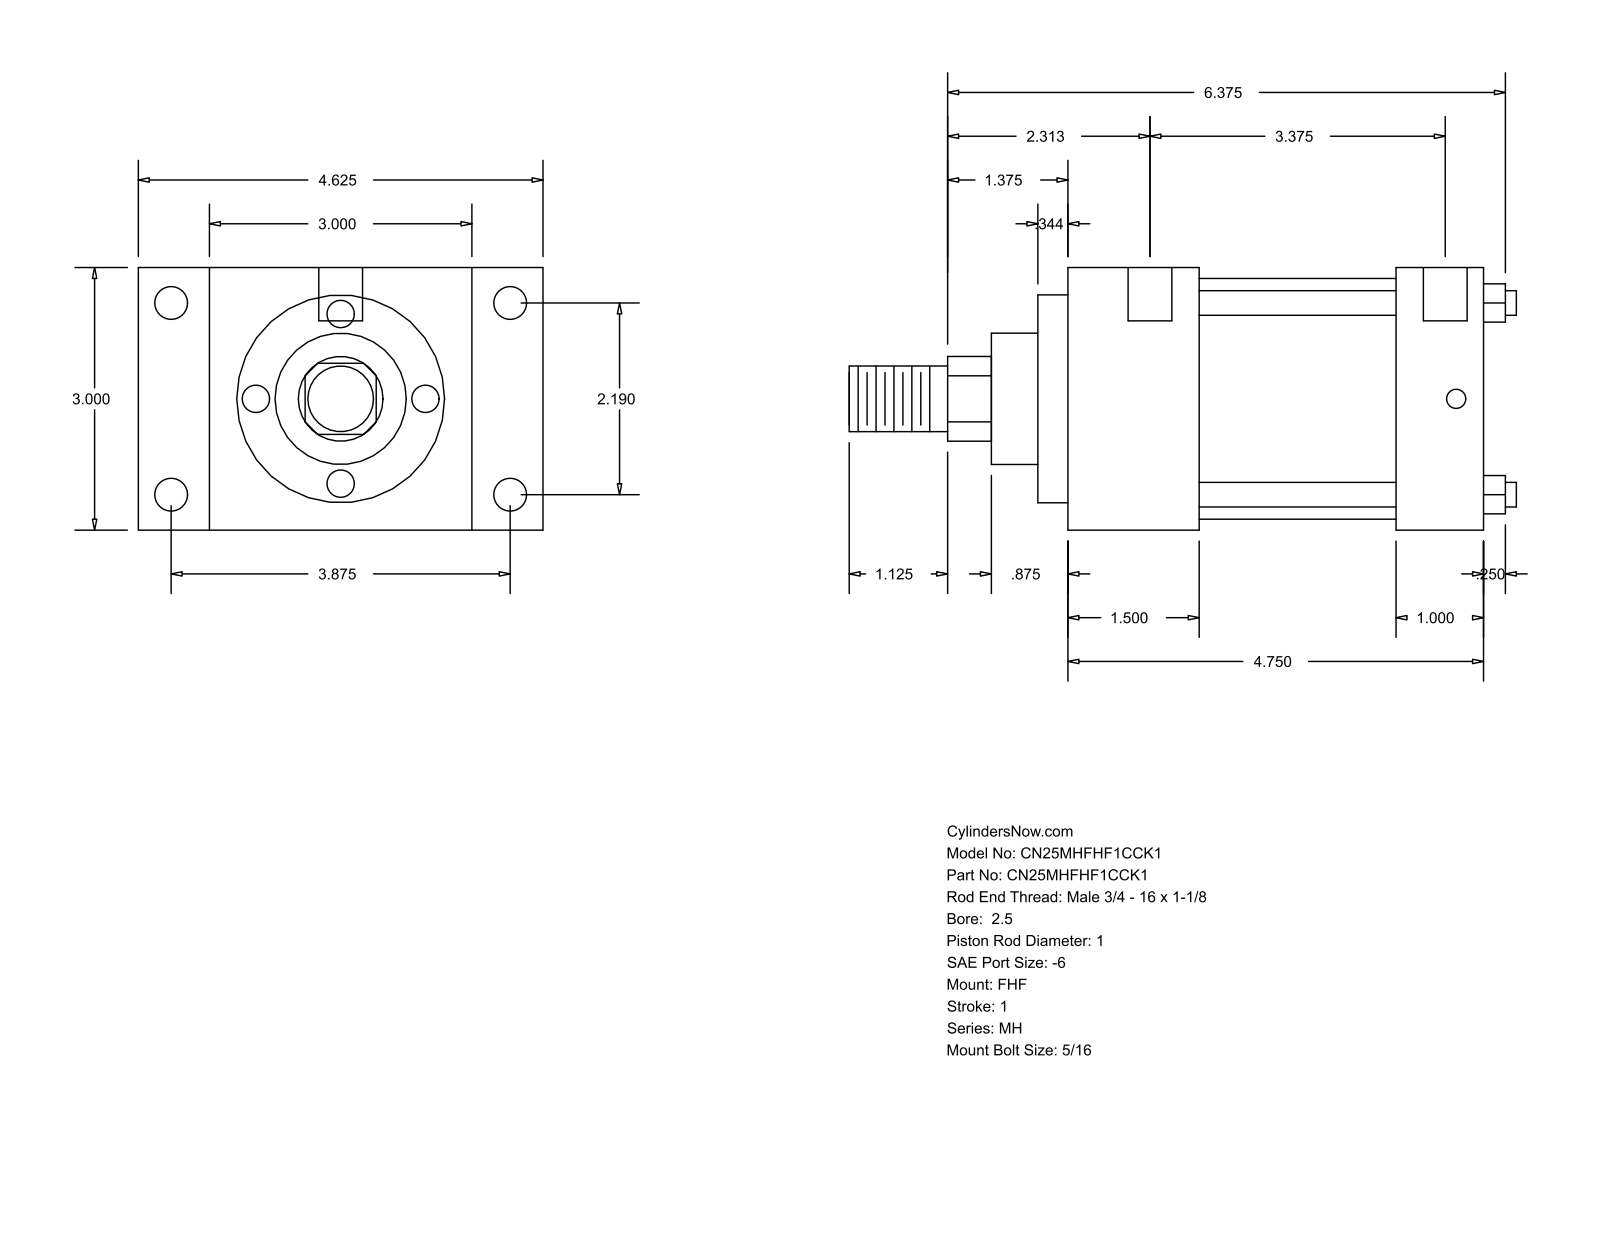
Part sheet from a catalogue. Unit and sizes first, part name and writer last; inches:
Units: inches
Overall size (bounding box): 7.625 × 4.625 × 3
Round holes (diameter × count): ⌀0.219 ×4, ⌀0.375 ×4, ⌀0.5 ×2
Round bosses / shafts (diameter × count): ⌀0.281 ×4, ⌀2.75 ×1, ⌀2.375 ×1, ⌀1.5 ×1, ⌀1 ×1, ⌀0.75 ×1
Partial cylindrical surfaces — rounded edges, fillets, slot ends (radius × count): R0.484 ×1
Main face-to-face distances: 3, 4.75, 1.5, 3.25, 0.813, 3.813, 4.625, 1, 3.75, 2.25
Hole centre spacings: 2.19, 3.687, 3.875, 4.451, 0.125, 0.187, 3.375, 3.5
Bodies: 0 solids, 90 faces (61 planar, 29 cylindrical, 0 other)
Part name (STEP PRODUCT): MH_FHF__0250_1
STEP written by: GSSL Pune (CONFIG_CONTROL_DESIGN)
